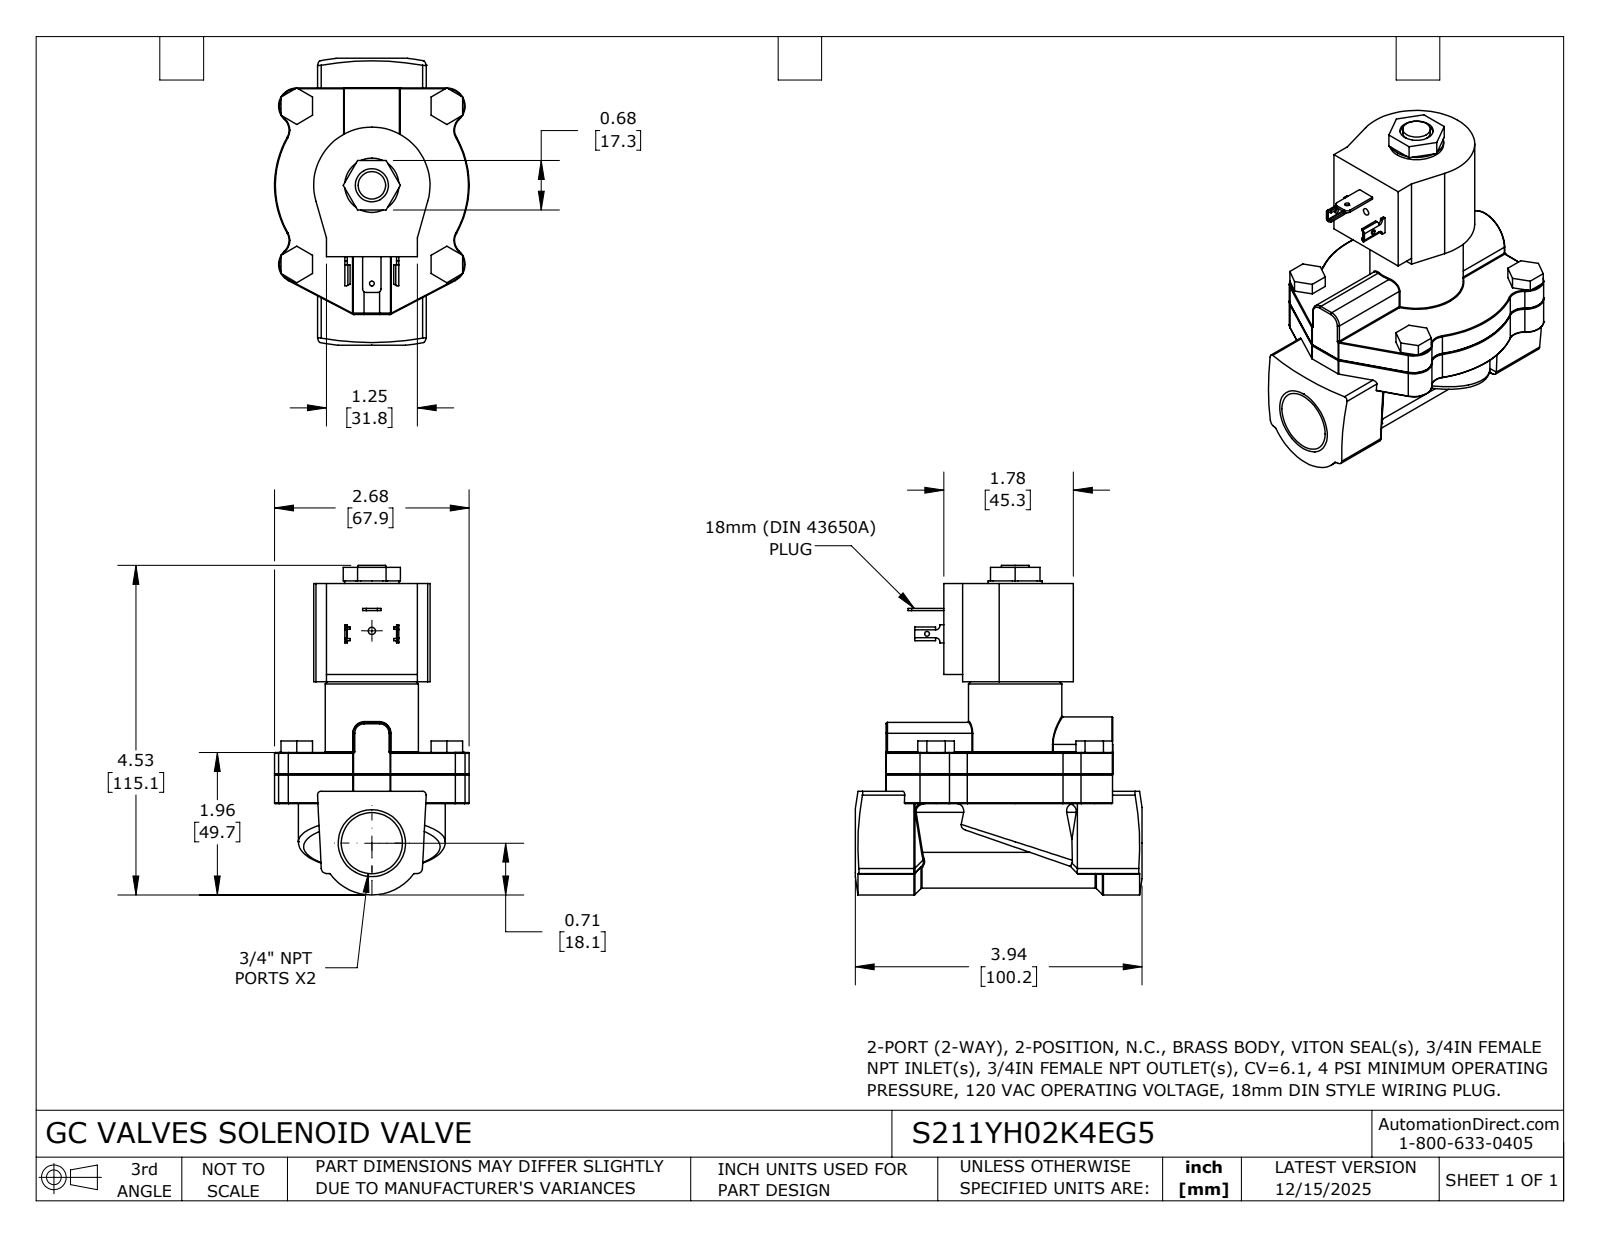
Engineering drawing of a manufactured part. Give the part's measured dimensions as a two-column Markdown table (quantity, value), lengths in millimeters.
| quantity | value |
| --- | --- |
| part name | S211YH02K4EG5 |
| STEP written by | SolidWorks 2024 (CONFIG_CONTROL_DESIGN) |
| units | millimeters |
| bodies | 1 solid, 443 faces (159 planar, 147 cylindrical, 137 other) |
| overall size | 115.1 × 100.2 × 67.9 |
| volume | 256 900 mm³ |
| surface area | 36 900 mm² |
| round holes (diameter × count) | 1.7 × 1, 1.7 × 1, 2.5 × 1, 11.6 × 1, 21.3 × 1 |
| round bosses / shafts (diameter × count) | 32.6 × 1, 18.9 × 1, 9.6 × 1 |
| partial cylindrical surfaces (radius × count) | 0.3 × 29, 0.5 × 14, 2.5 × 6, 0.2 × 4, 1 × 4, 1.3 × 4, 5.1 × 4, 6.4 × 4 |
| main face-to-face distances | 17.8, 76.8, 59, 4.3, 13.5, 72.5, 58.9, 42.5, 38.2, 24.7 |
| hole center spacings | 34.3, 74.1 |
